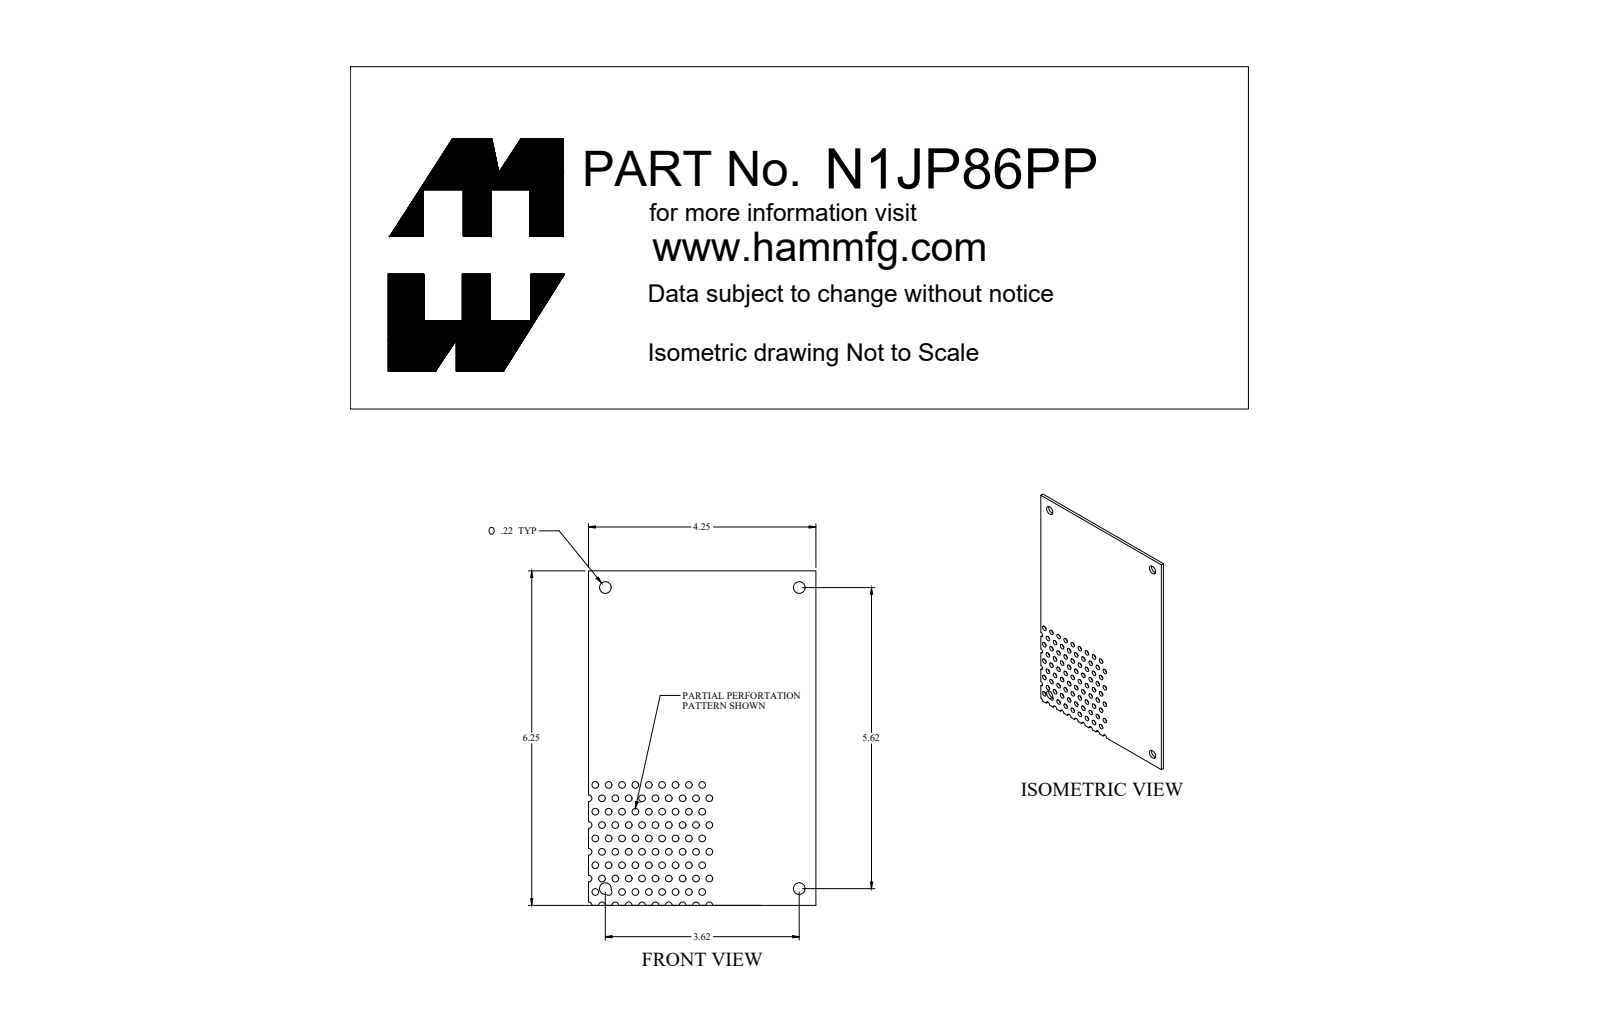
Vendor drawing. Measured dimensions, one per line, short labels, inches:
name: N1JP86PP
written by: SolidWorks 2018 (AUTOMOTIVE_DESIGN)
unit: in
bodies: 1 solid, 203 faces (19 planar, 184 cylindrical, 0 other)
size: 6.25 × 4.25 × 0.072
volume: 1.825 in³; area: 54.73 in²
holes: 62× ⌀0.125, 18× ⌀0.125, 4× ⌀0.218
rounds: 13× R0.062, 2× R0.063
face distances: 0.072, 4.25, 6.25
hole spacings: 0.25, 0.5, 0.559, 0.707, 0.28, 0.75, 0.451, 0.902
